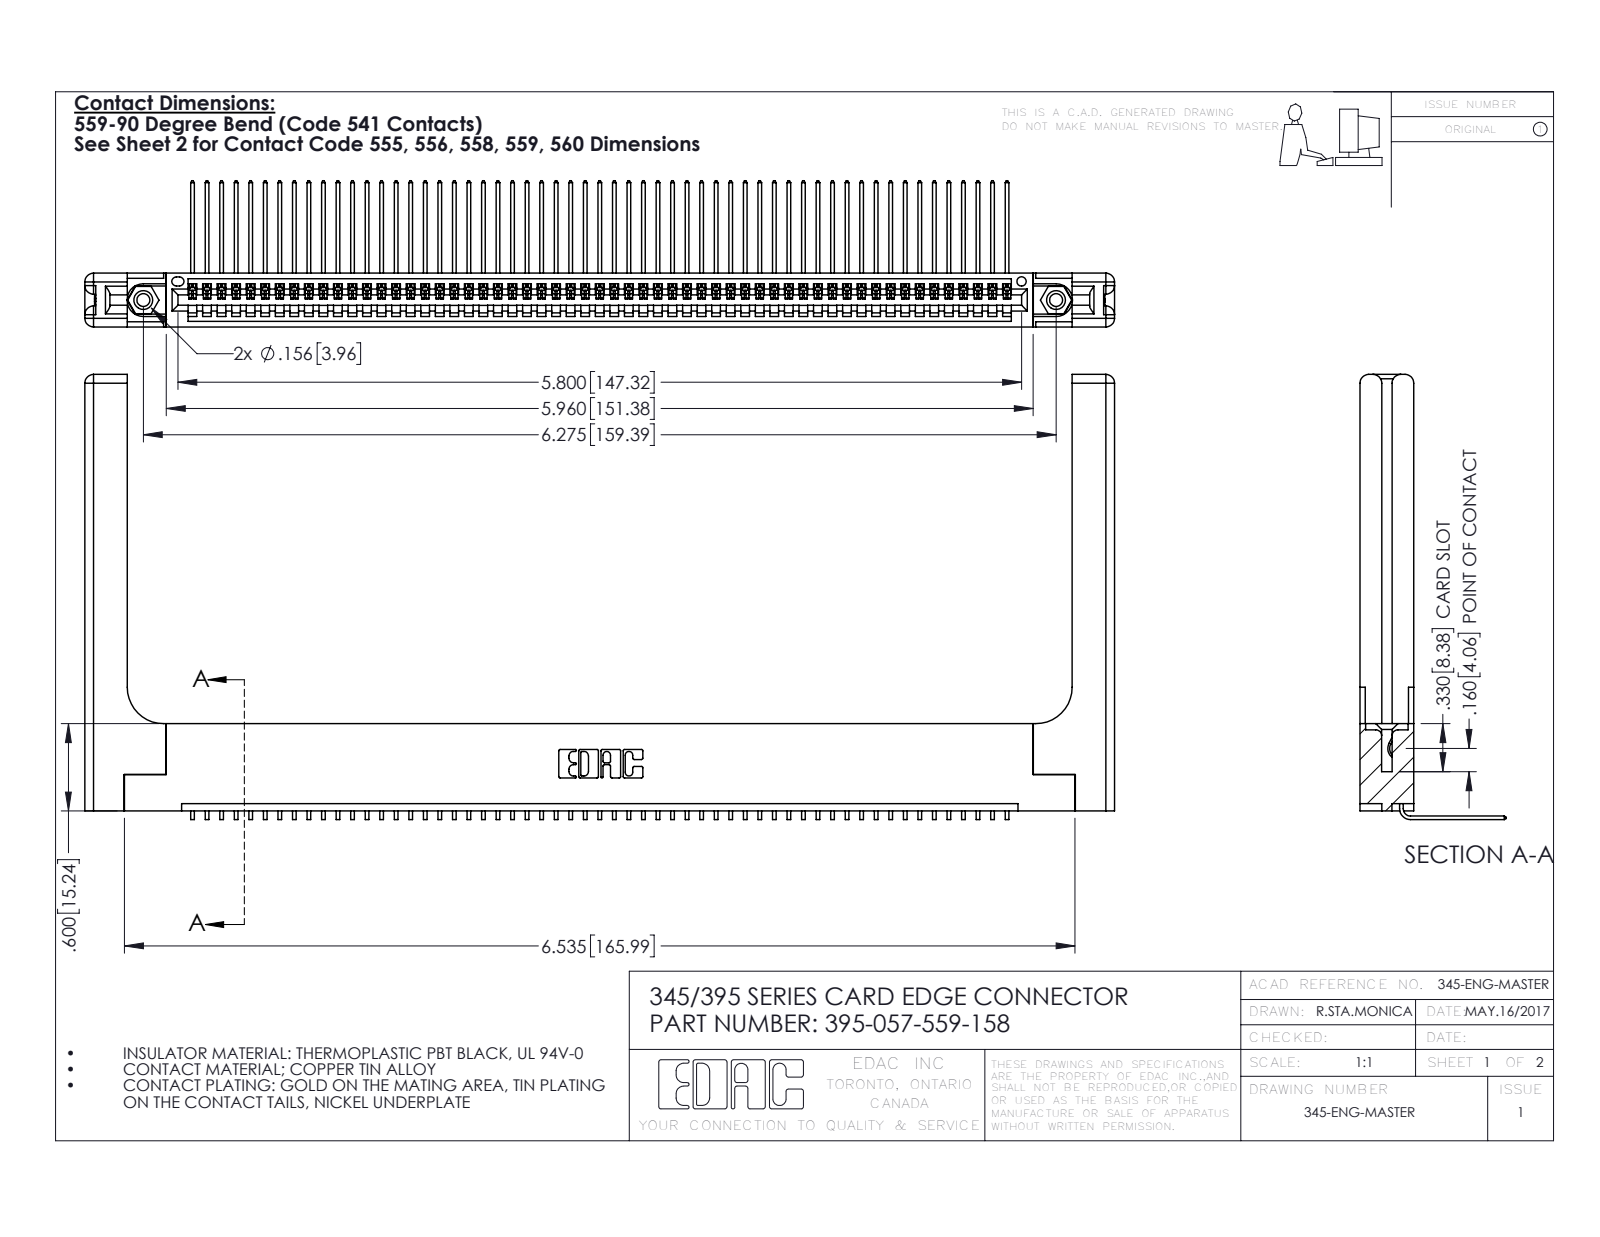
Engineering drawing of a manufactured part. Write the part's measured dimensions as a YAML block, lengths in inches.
part_name: "345-220-058_345-220-058; 395-057-559-158; 345-250-001_345-250-001-102; 345-292-001_558 559 Tail - 1 (+1 more)"
step_written_by: "SolidWorks 2016 (CONFIG_CONTROL_DESIGN)"
units: inches
bodies: {solids: 62, faces: 3802, planar: 2622, cylindrical: 1120, other: 60}
overall_size: [7.079, 3.059, 1.005]
volume: 1.58
surface_area: 46.09
round_holes:
  - {diameter: 0.089, count: 2}
  - {diameter: 0.125, count: 2}
  - {diameter: 0.156, count: 2}
  - {diameter: 0.064, count: 1}
round_bosses_or_shafts:
  - {diameter: 0.155, count: 2}
partial_cylinders:
  - {radius: 0.006, count: 114}
  - {radius: 0.01, count: 22}
  - {radius: 0.06, count: 16}
  - {radius: 0.007, count: 6}
  - {radius: 0.031, count: 6}
  - {radius: 0.026, count: 3}
  - {radius: 0.03, count: 2}
  - {radius: 0.031, count: 2}
face_to_face_distances: [0.072, 0.37, 0.298, 0.2, 0.098, 0.272, 0.025, 0.225, 0.148, 0.15]
hole_center_spacings: [0.27, 6.039, 6.275]
